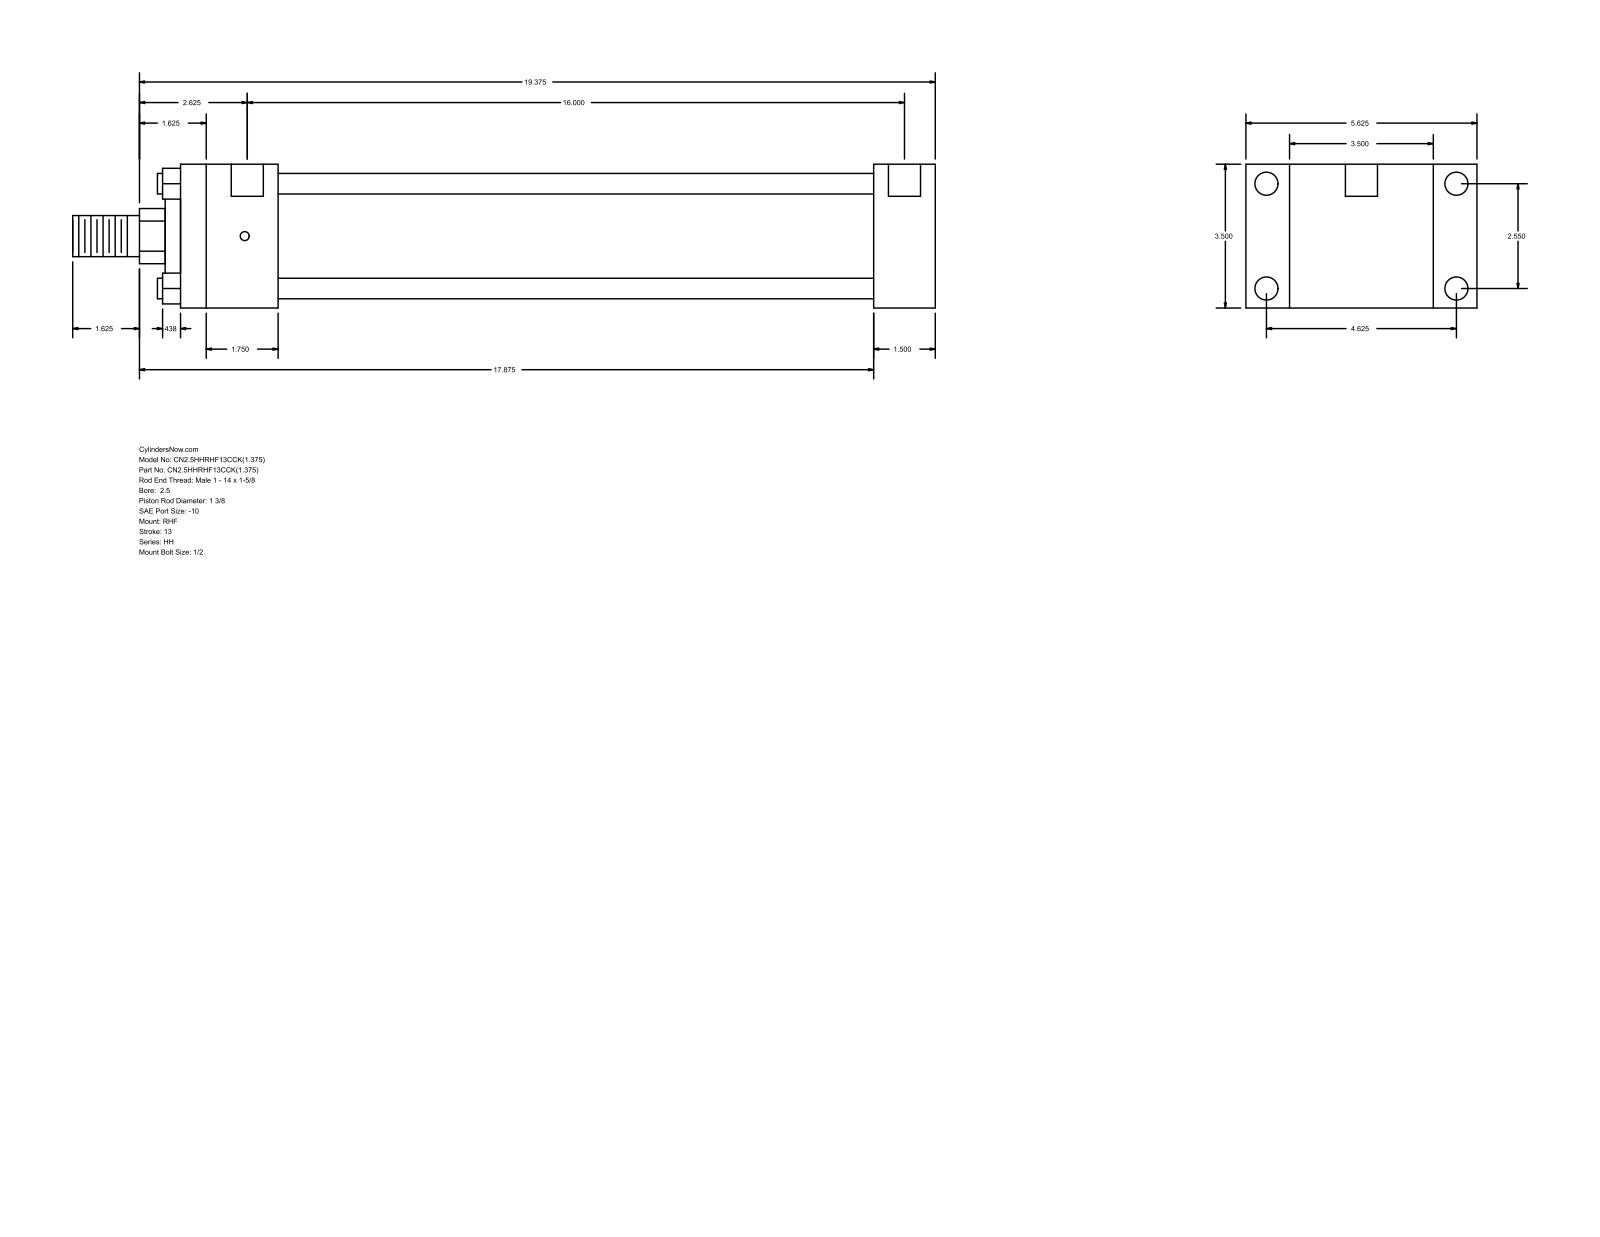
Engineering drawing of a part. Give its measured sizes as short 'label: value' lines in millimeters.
name: HH_RHF__0250_1.375
written by: GSSL Pune (CONFIG_CONTROL_DESIGN)
unit: mm
bodies: 0 solids, 88 faces (60 planar, 28 cylindrical, 0 other)
size: 533.4 × 142.88 × 88.9
holes: 4× ⌀5.56, 4× ⌀14.3, 2× ⌀19.84
bosses: 4× ⌀12.7, 1× ⌀73.03, 1× ⌀50.8, 1× ⌀34.92, 1× ⌀25.4
rounds: 1× R17.06
face distances: 88.9, 38.1, 26.99, 115.89, 428.62, 466.72, 142.88, 60.32, 368.3, 406.4
hole spacings: 64.76, 117.48, 134.15, 409.57, 1.58, 1.59, 406.4, 407.98
